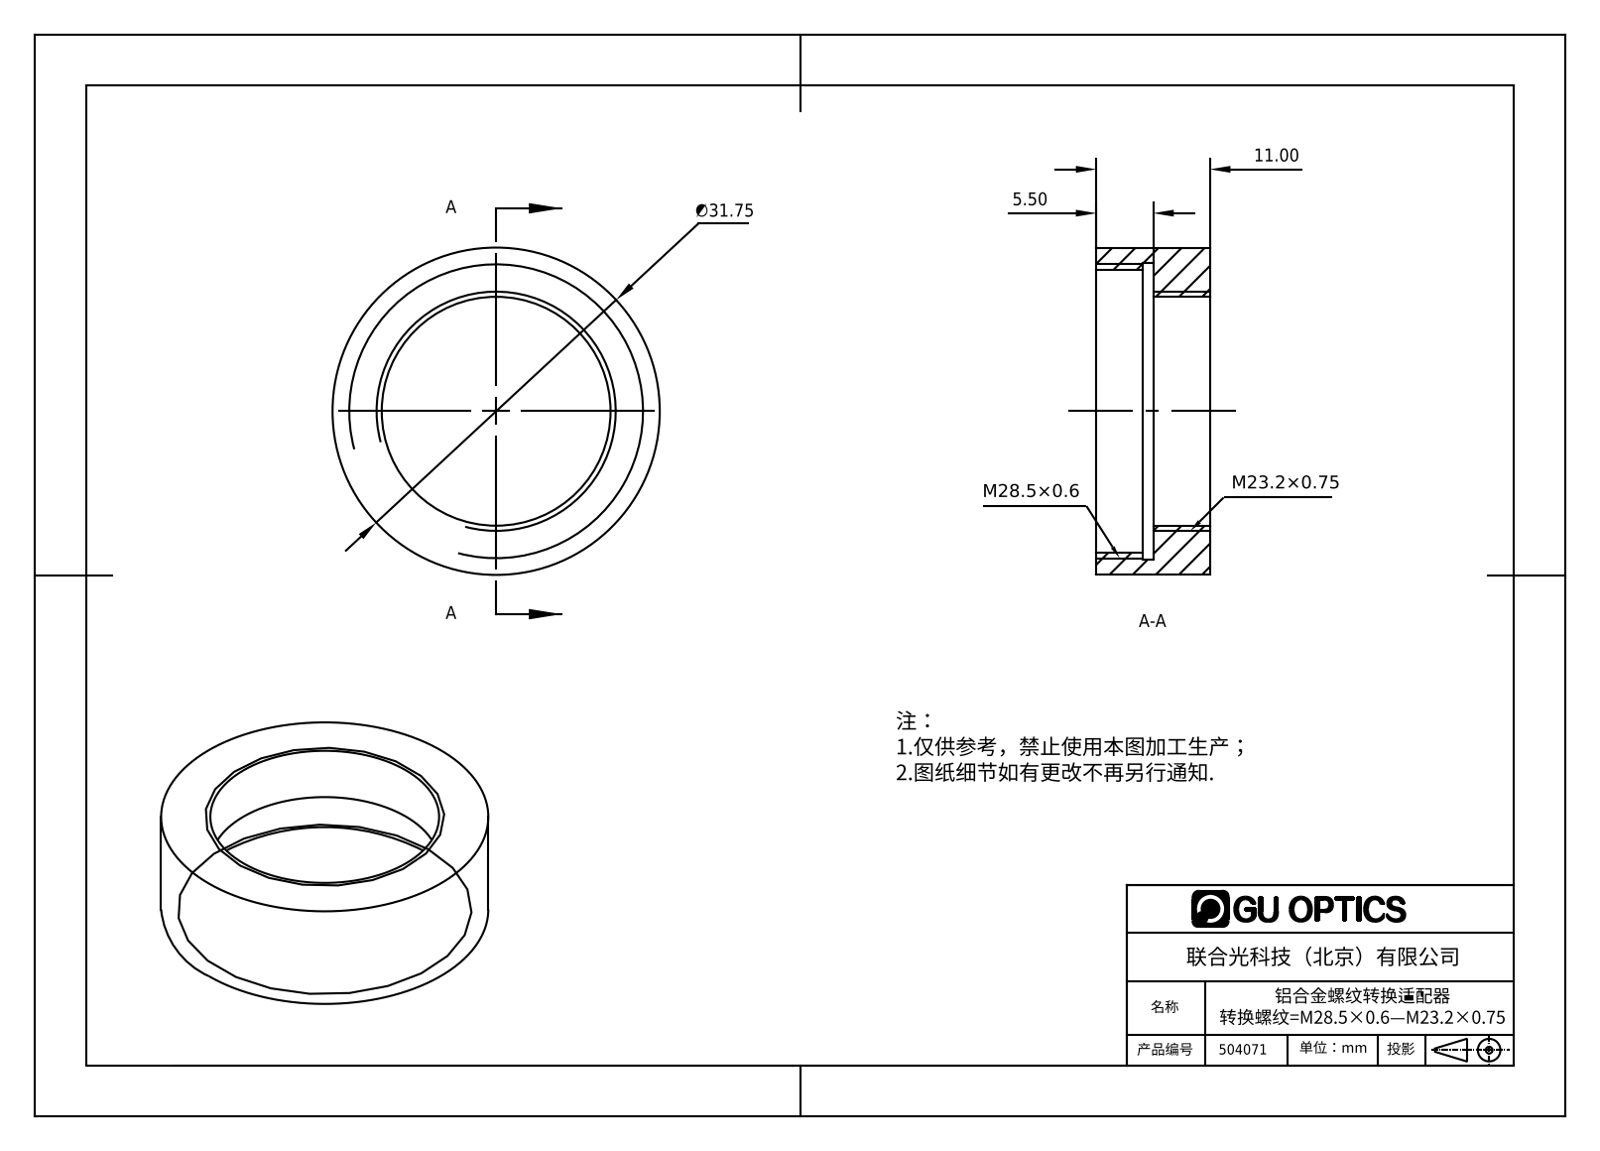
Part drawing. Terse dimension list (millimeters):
name: 504071
written by: SolidWorks 2016 (AUTOMOTIVE_DESIGN)
unit: mm
bodies: 1 solid, 12 faces (4 planar, 8 cylindrical, 0 other)
size: 31.75 × 31.75 × 11
volume: 3 260 mm³; area: 2 875 mm²
holes: 1× ⌀22.2, 1× ⌀27.5, 1× ⌀28.7
bosses: 1× ⌀31.75
face distances: 5.5, 11, 4.5, 1, 6.5
